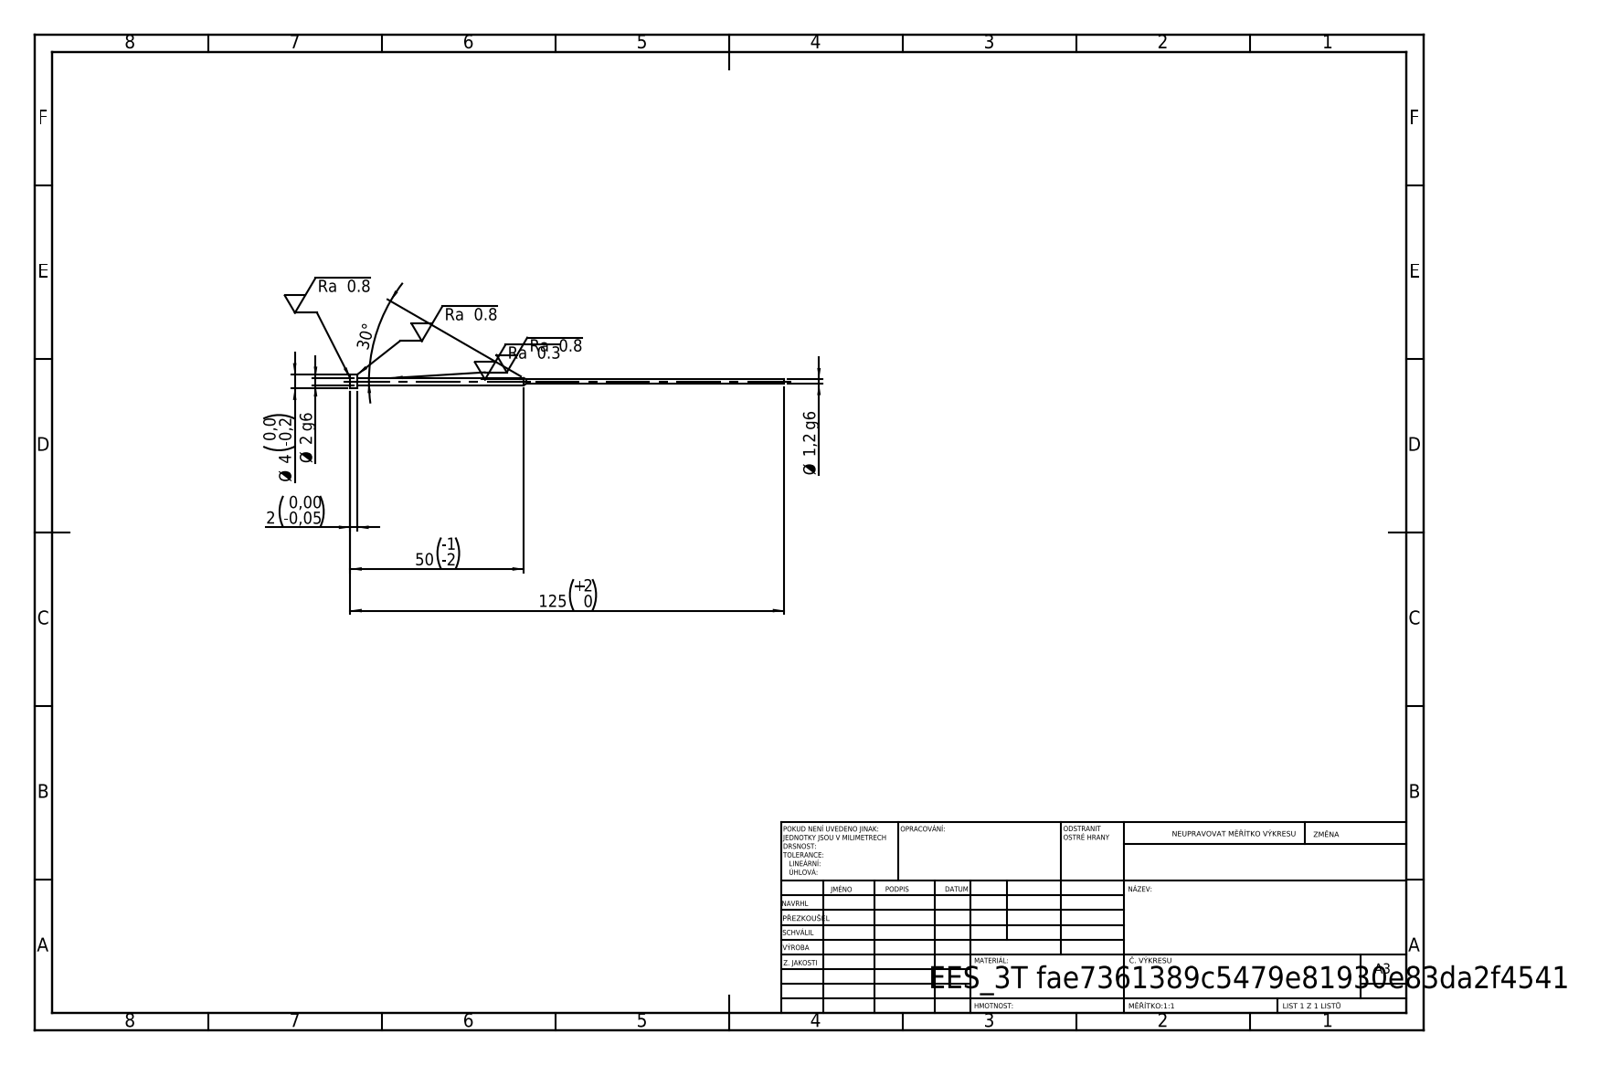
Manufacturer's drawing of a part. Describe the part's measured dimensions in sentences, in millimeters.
Its 3-D file was written by "SolidWorks 2019 (CONFIG_CONTROL_DESIGN)". It is 1 solid with 11 faces: 3 planar, 6 cylindrical and 2 other. Overall it measures 125 by 4 by 4 millimeters. Its volume is 261 cubic millimeters and its surface area 634 square millimeters. Round bosses or shafts: 1 of diameter 4, 1 of diameter 2, 1 of diameter 1.2. The main face-to-face distances are 2, 123, 125.
